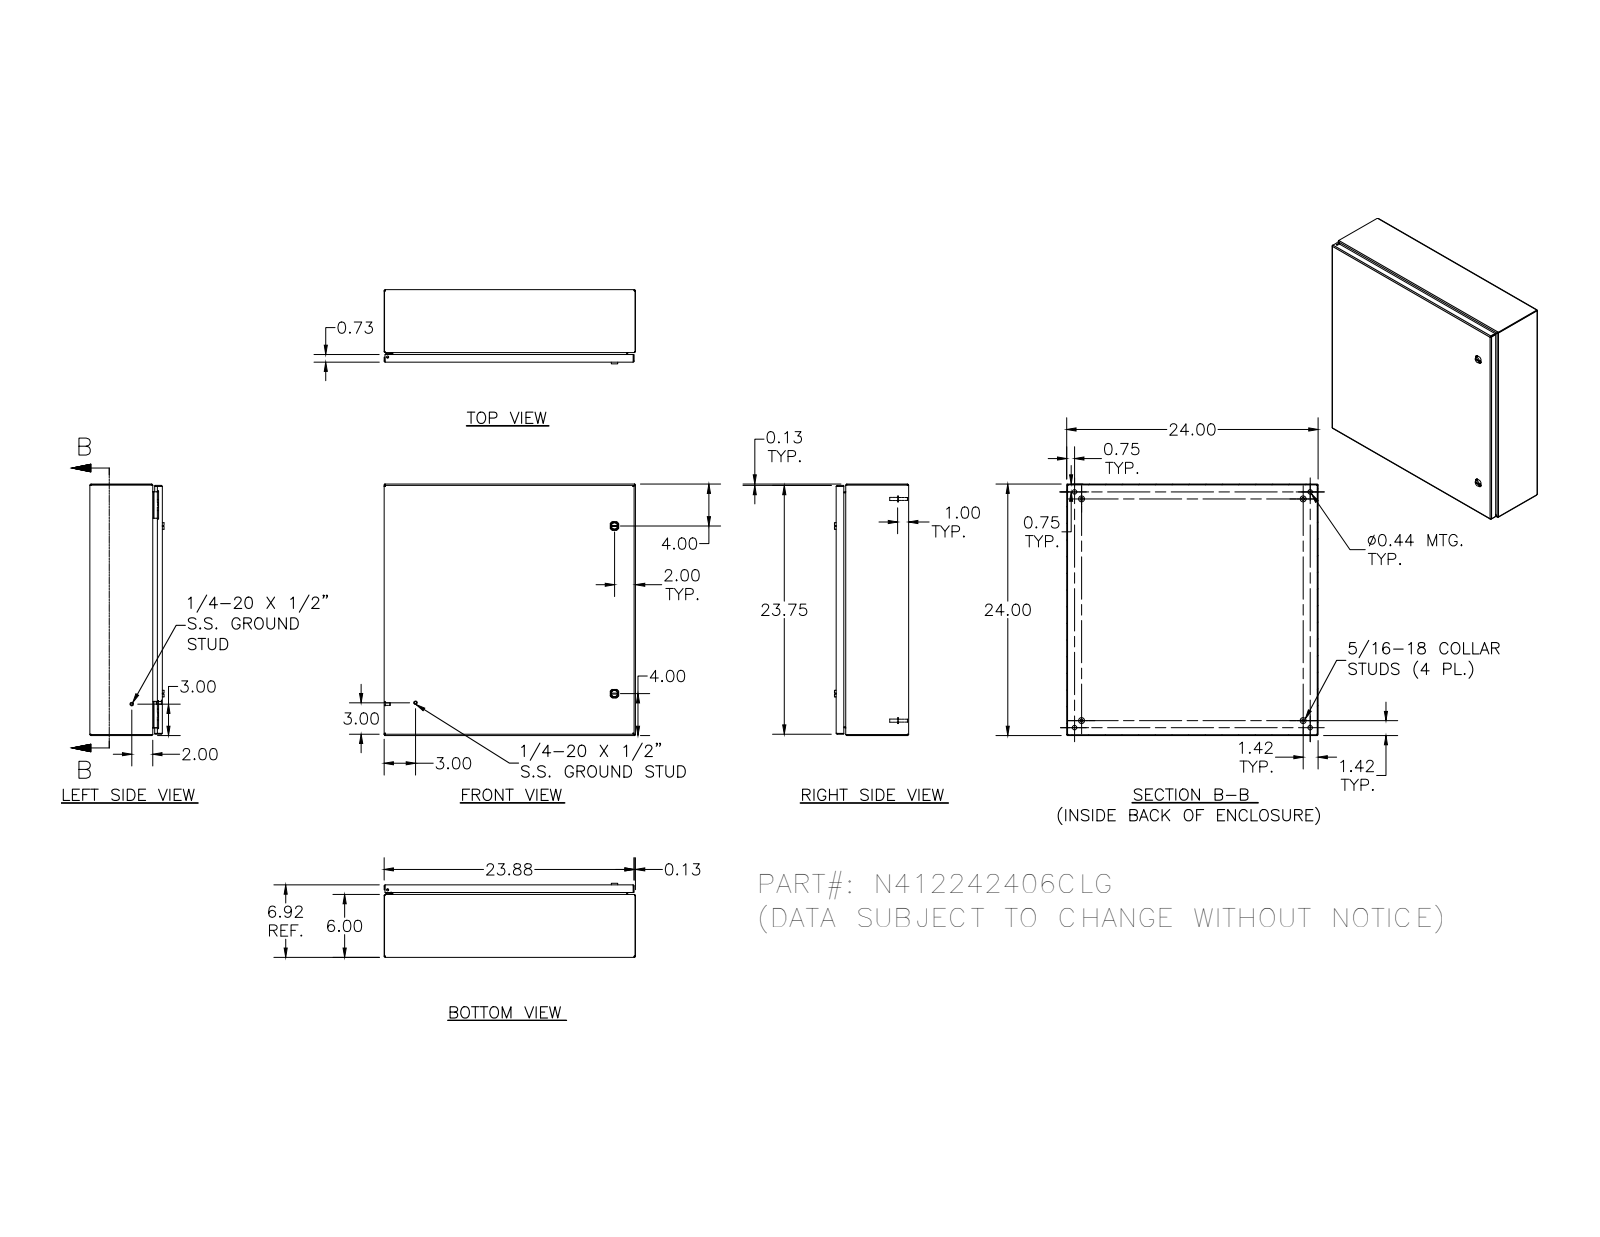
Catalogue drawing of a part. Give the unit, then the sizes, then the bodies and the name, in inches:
Units: inches
Overall size (bounding box): 24 × 24 × 7.075
Round holes (diameter × count): ⌀0.188 ×5, ⌀0.093 ×4, ⌀0.152 ×4, ⌀0.167 ×4, ⌀0.172 ×4, ⌀0.437 ×4, ⌀0.156 ×2, ⌀0.197 ×2, ⌀0.315 ×2, ⌀0.394 ×2, ⌀0.402 ×2, ⌀0.634 ×2
Round bosses / shafts (diameter × count): ⌀0.25 ×10, ⌀0.563 ×4, ⌀0.36 ×4, ⌀0.32 ×4, ⌀0.3 ×4, ⌀0.256 ×4, ⌀0.164 ×4, ⌀0.131 ×4
Partial cylindrical surfaces — rounded edges, fillets, slot ends (radius × count): R0.012 ×54, R0.031 ×30, R0.05 ×26, R0.02 ×23, R0.105 ×20, R0.016 ×18, R0.125 ×16, R0.032 ×8
Main face-to-face distances: 0.074, 6.843, 6.769, 6.917, 0.074, 23.926, 23.926, 24, 23.852, 0.917
Hole centre spacings: 20, 0.66, 0.656, 1.307, 1.965, 19.34, 20.66, 1.619
Volume: 142.8 in³ · Surface area: 3 875 in²
Bodies: 40 solids, 1812 faces (704 planar, 676 cylindrical, 432 other)
Part name (STEP PRODUCT): N412242406CLG
STEP written by: SolidWorks 2018 (AUTOMOTIVE_DESIGN)
